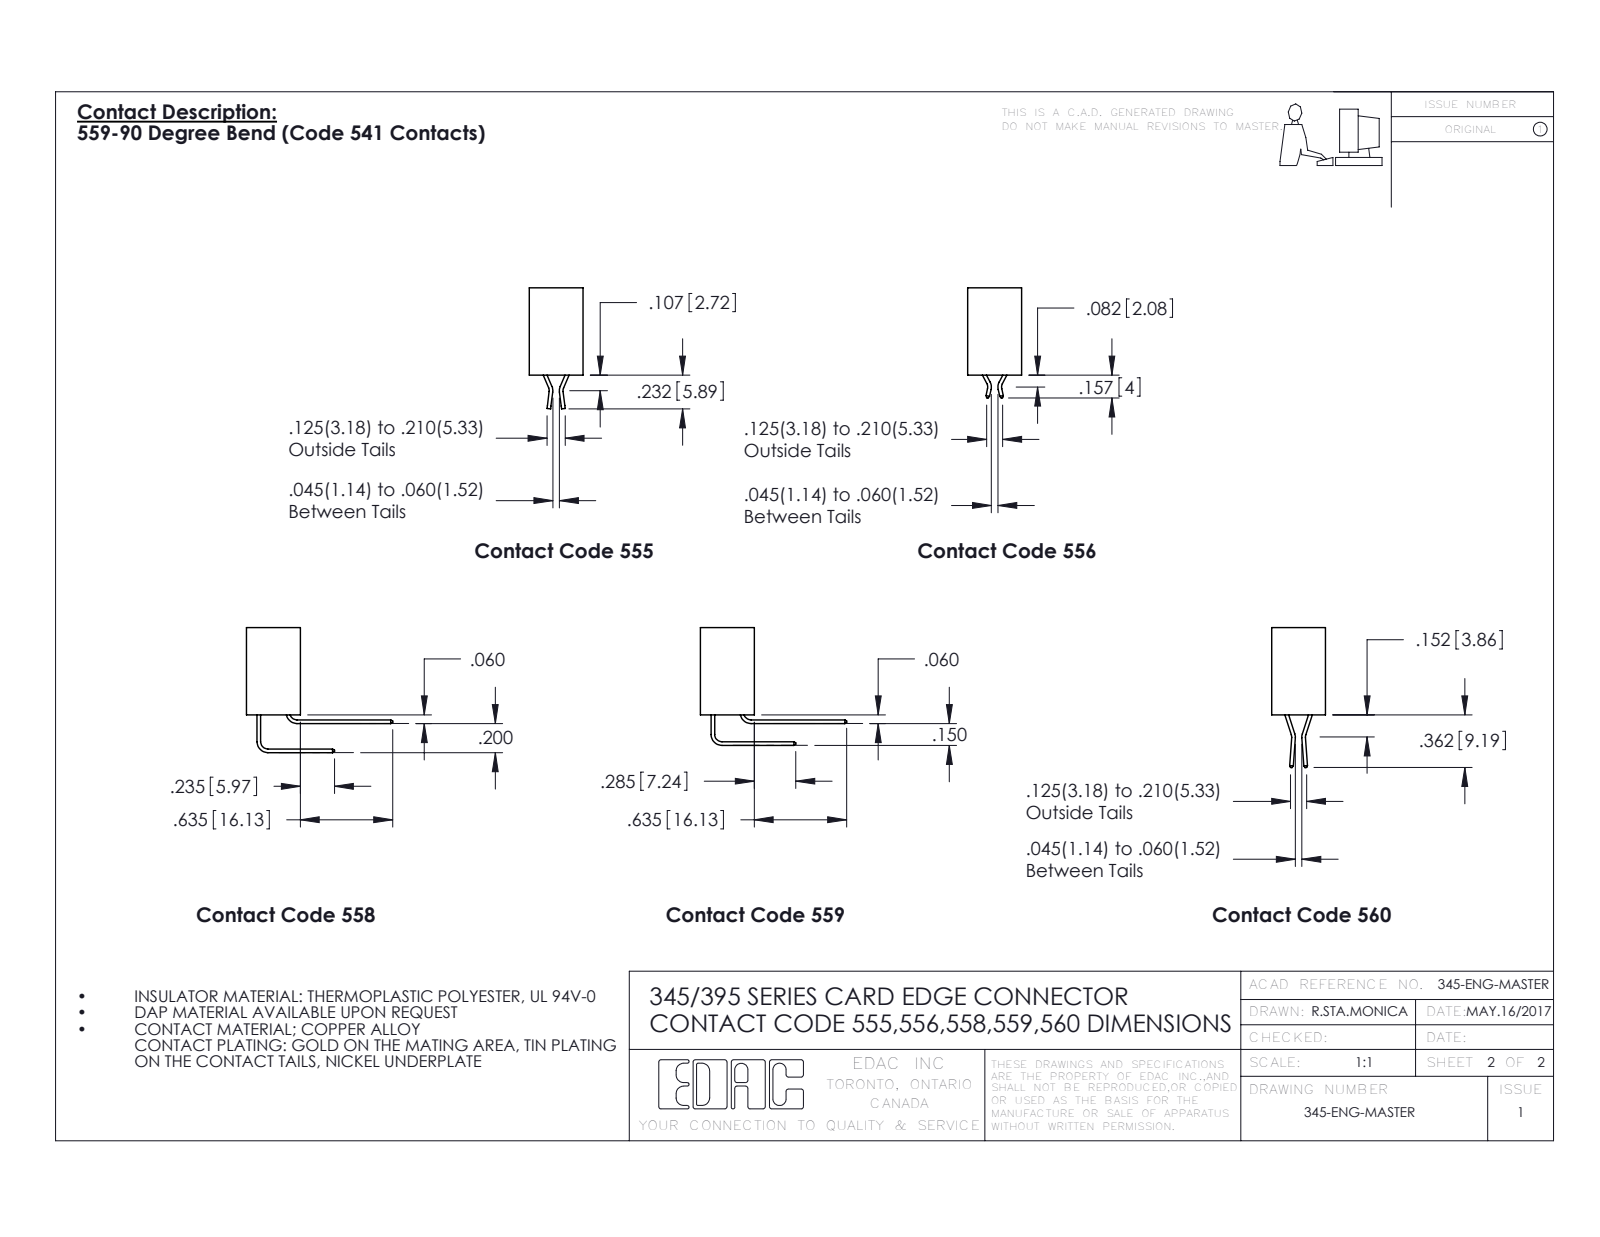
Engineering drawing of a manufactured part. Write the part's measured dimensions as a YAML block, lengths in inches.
part_name: "345-292-001_556 Tail; 395-024-556-201; 345 Part_No Mounting Lugs"
step_written_by: "SolidWorks 2016 (CONFIG_CONTROL_DESIGN)"
units: inches
bodies: {solids: 25, faces: 1462, planar: 964, cylindrical: 498, other: 0}
overall_size: [1.46, 0.757, 0.37]
volume: 0.24
surface_area: 8.561
round_holes:
  - {diameter: 0.064, count: 1}
partial_cylinders:
  - {radius: 0.006, count: 36}
  - {radius: 0.01, count: 22}
  - {radius: 0.007, count: 6}
  - {radius: 0.031, count: 6}
  - {radius: 0.026, count: 3}
  - {radius: 0.01, count: 2}
  - {radius: 0.014, count: 2}
  - {radius: 0.019, count: 2}
face_to_face_distances: [0.2, 0.298, 0.072, 0.37, 0.025, 0.098, 0.272, 0.1, 0.225, 0.3]
